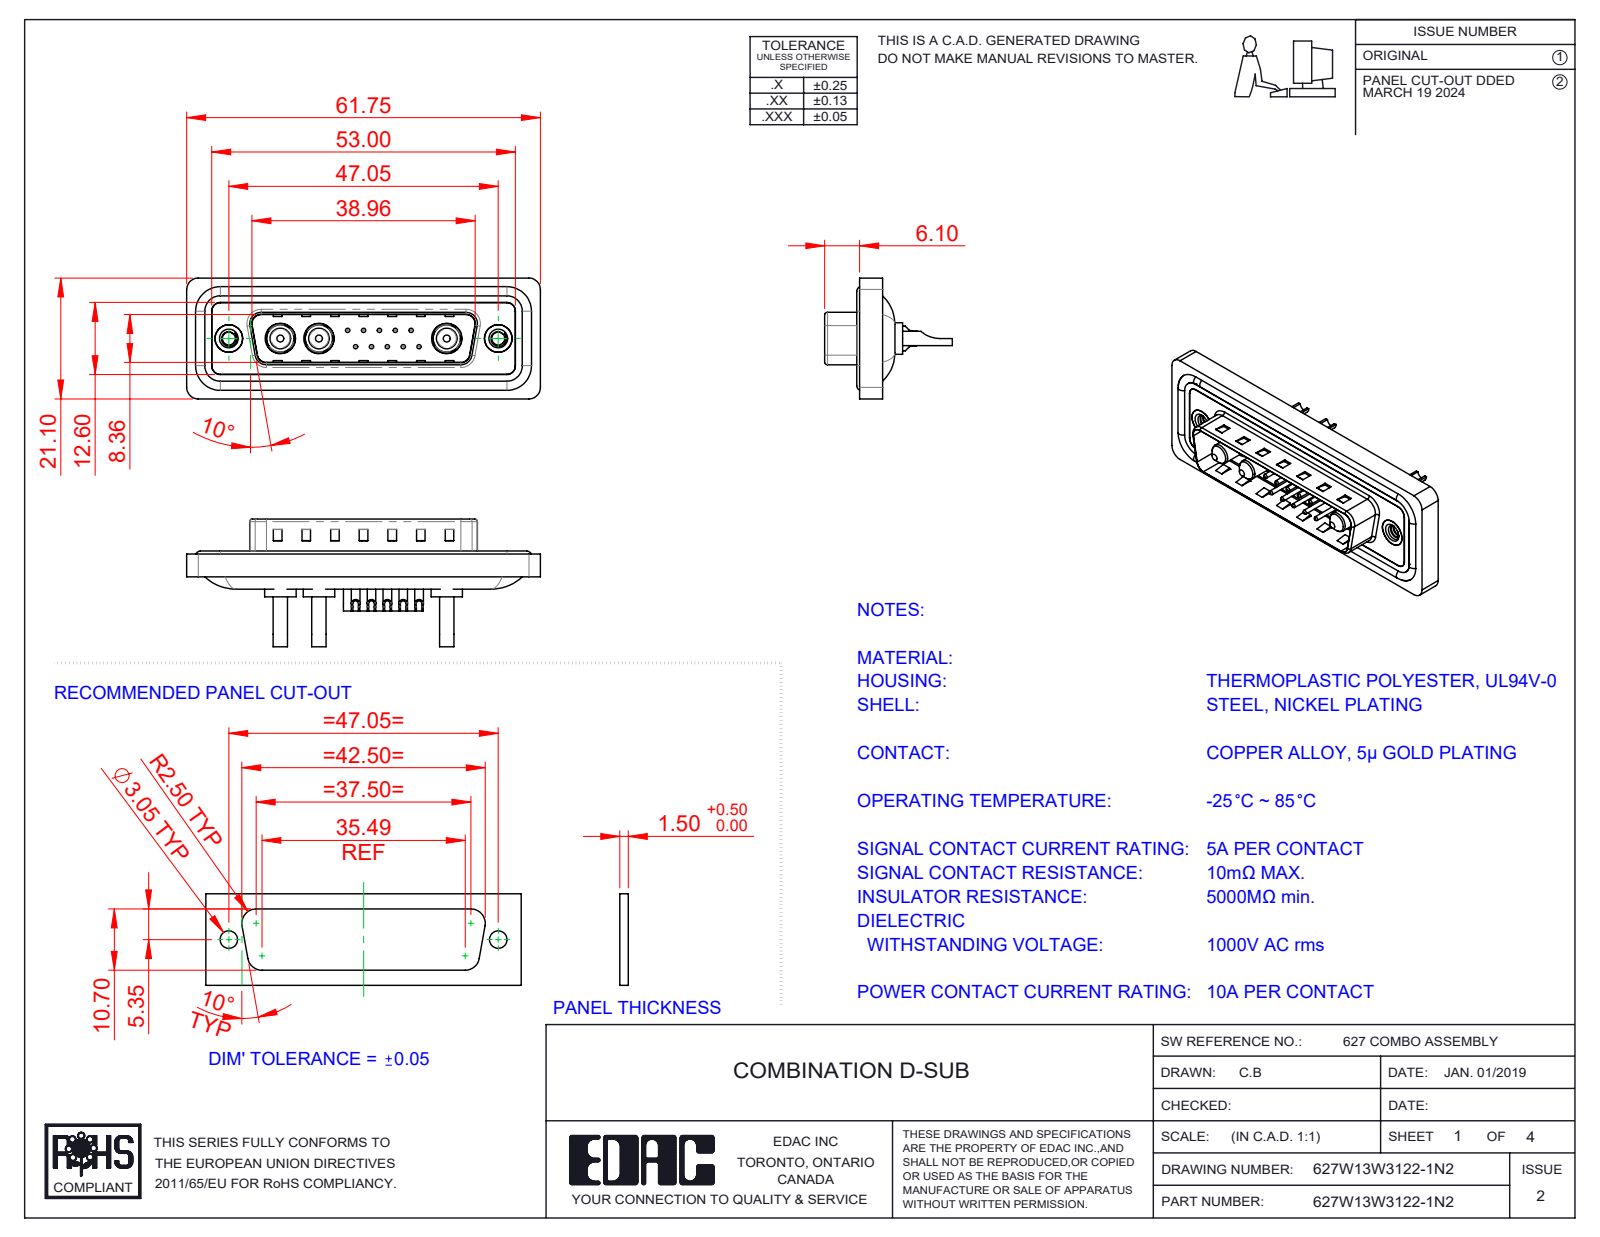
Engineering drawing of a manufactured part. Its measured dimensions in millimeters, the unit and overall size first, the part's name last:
Units: millimetres
Overall size (bounding box): 61.75 × 22.3 × 21.1
Round holes (diameter × count): ⌀0.75 ×10, ⌀1 ×10, ⌀1.6 ×10, ⌀2 ×10, ⌀1.7 ×3, ⌀4.85 ×3, ⌀5.3 ×3, ⌀2.26 ×2, ⌀4 ×2, ⌀4.8 ×2, ⌀5 ×2
Round bosses / shafts (diameter × count): ⌀1.5 ×10, ⌀1.6 ×4, ⌀5.5 ×3, ⌀5.2 ×3, ⌀4.75 ×3, ⌀3.75 ×3, ⌀3.6 ×3, ⌀2.5 ×3
Partial cylindrical surfaces — rounded edges, fillets, slot ends (radius × count): R1.5 ×22, R2 ×18, R0.5 ×8, R1.6 ×8, R1 ×6, R0.25 ×4, R0.6 ×4, R0.65 ×4
Main face-to-face distances: 0.4, 1.5, 1.1, 1.6, 0.5, 3.1, 2.9, 0.82, 9.58, 4.1
Hole centre spacings: 3.16, 2.77, 5.04, 5.54, 7.49, 5.03, 8.31, 10.11
Volume: 7 342 mm³ · Surface area: 12 097 mm²
Bodies: 23 solids, 985 faces (335 planar, 414 cylindrical, 236 other)
Part name (STEP PRODUCT): 627Combo Contact Row 2_22; 627Combo Housing_13W3; 627Combo Waterproof Housing_25 Contacts; 627Combo Shell Rear_25 Contacts (+5 more)
STEP written by: SolidWorks 2023 (CONFIG_CONTROL_DESIGN)
